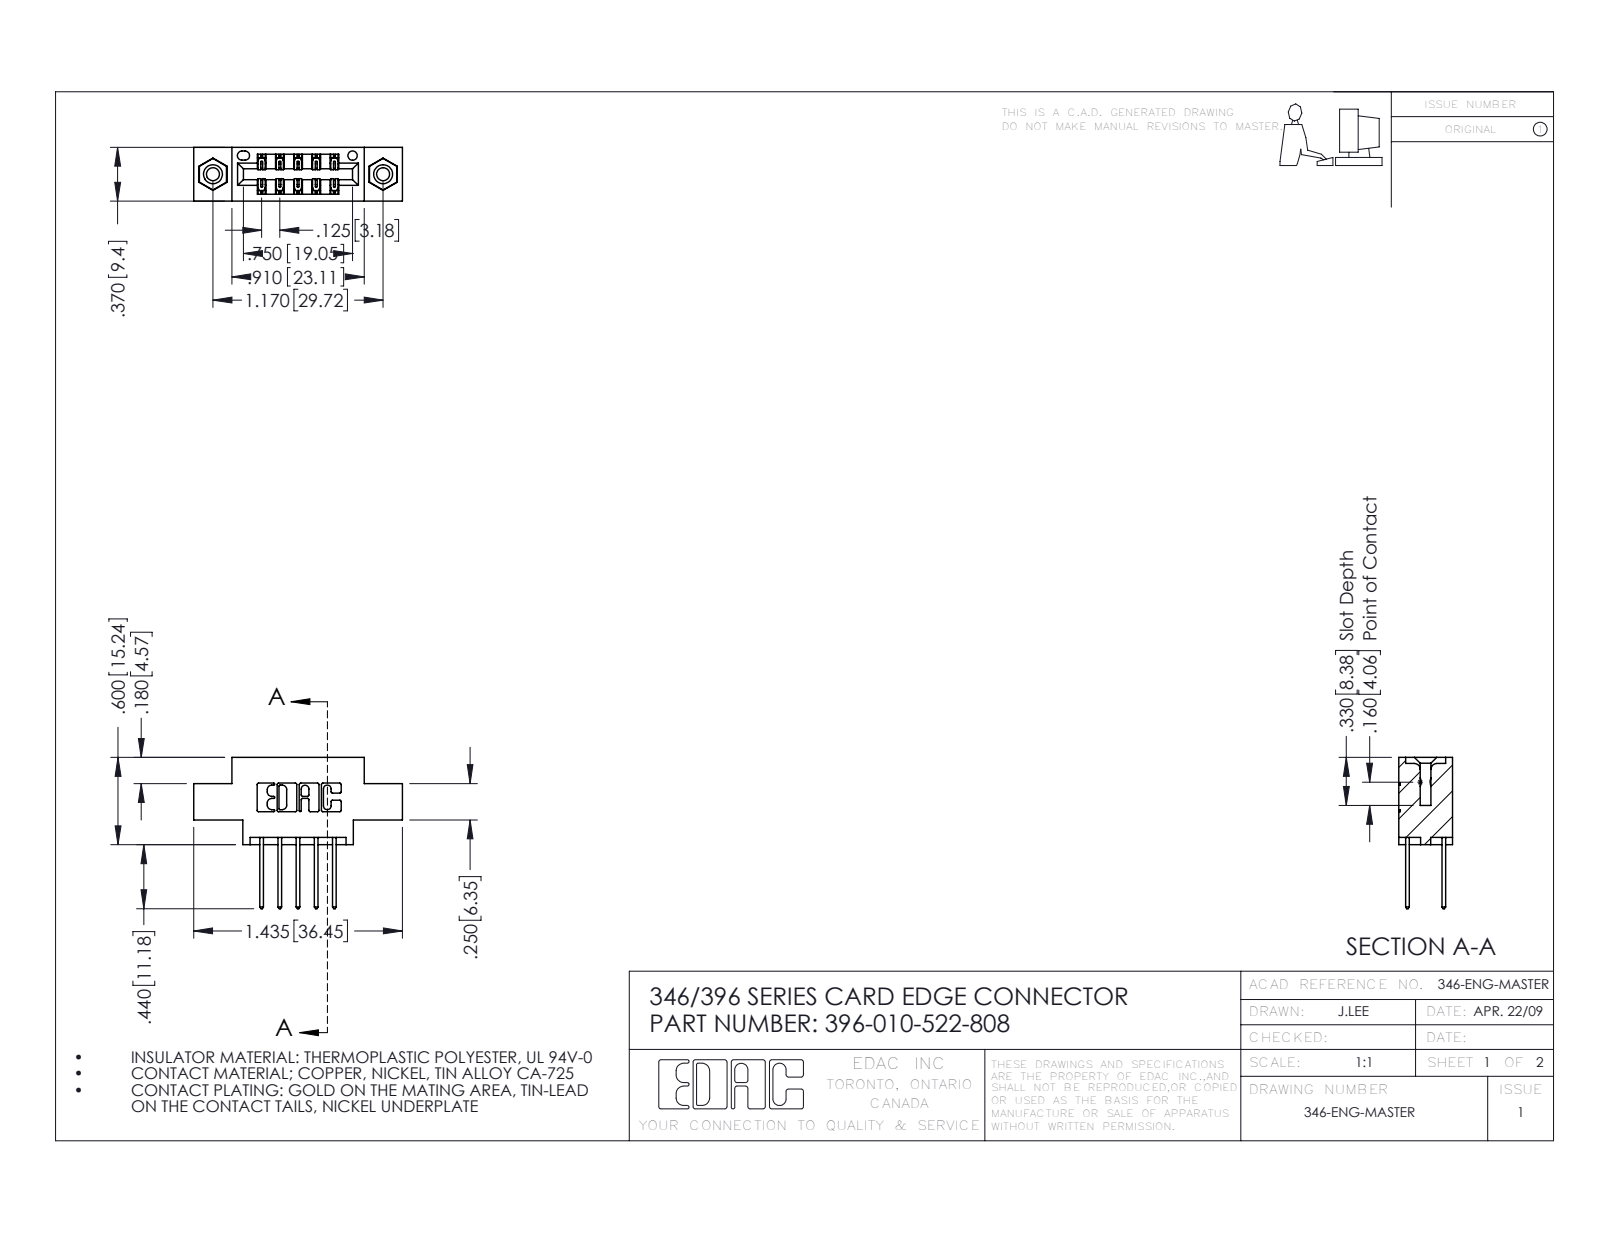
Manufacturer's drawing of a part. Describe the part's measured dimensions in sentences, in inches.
The part is named "345-292-001_345-293-122; 396-010-522-808; 346 Part_0.170 Offset - 0.156 Dia-TI; 345-250-001_345-250-003-102". Its 3-D file was written by "SolidWorks 2016 (CONFIG_CONTROL_DESIGN)". It is 13 solids with 706 faces: 462 planar, 228 cylindrical and 16 other. Overall it measures 1.435 by 1.04 by 0.37 inches. Its volume is 0.191 cubic inches and its surface area 6.264 square inches. Round holes: 2 of diameter 0.089, 2 of diameter 0.125, 2 of diameter 0.156, 1 of diameter 0.064. Round bosses or shafts: 2 of diameter 0.155. Partial cylindrical surfaces (rounded edges, fillets, slot ends): 22 of radius 0.01, 15 of radius 0.006, 10 of radius 0.01, 6 of radius 0.007, 6 of radius 0.031, 3 of radius 0.026, 2 of radius 0.014, 2 of radius 0.022. The main face-to-face distances are 0.25, 0.37, 0.048, 0.322, 0.025, 0.072, 0.298, 0.222, 0.148, 0.275. The hole center spacings are 0.246, 0.969, 1.17.
